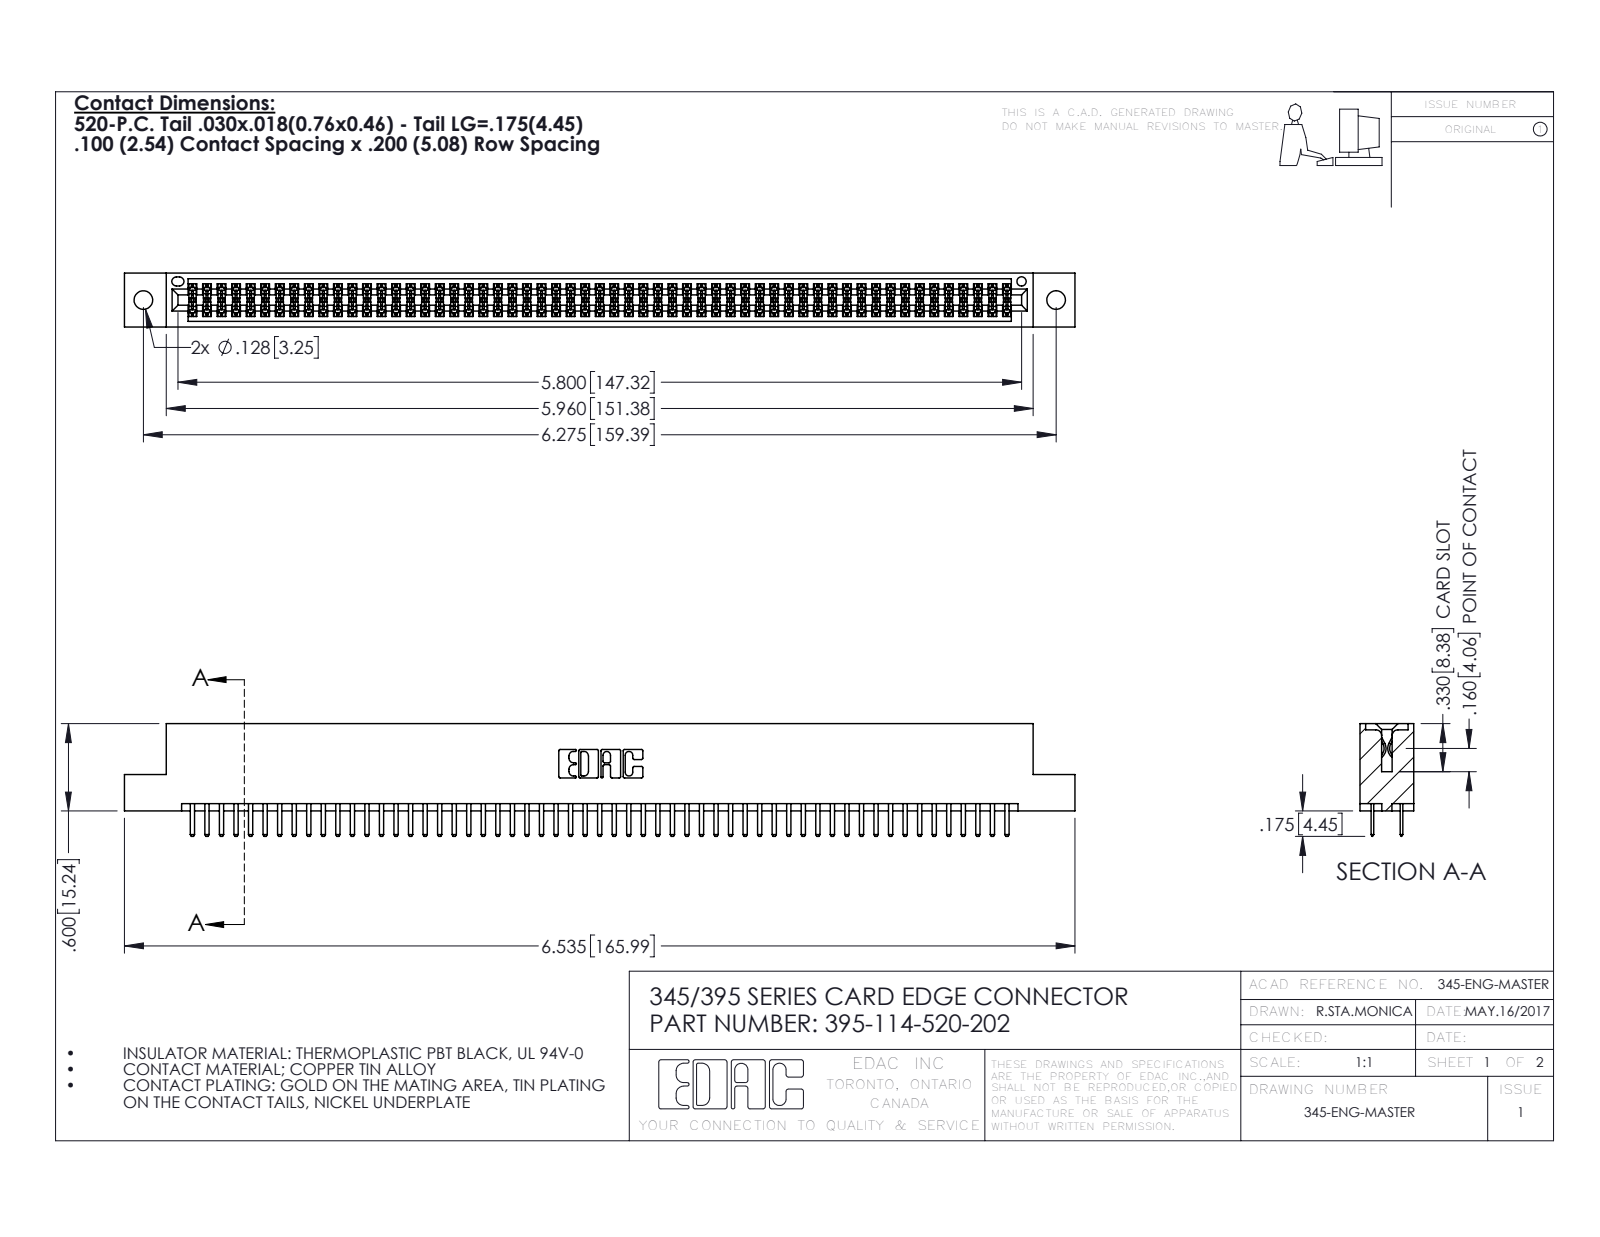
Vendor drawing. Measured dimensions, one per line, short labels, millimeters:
name: 345-292-001_345-293-120; 345 Part_Flush Mounting Lugs - 0.128 Dia; 395-114-520-202
written by: SolidWorks 2016 (CONFIG_CONTROL_DESIGN)
unit: mm
bodies: 115 solids, 6282 faces (4070 planar, 2212 cylindrical, 0 other)
size: 166 × 19.7 × 9.4
volume: 16 200 mm³; area: 23 830 mm²
holes: 2× ⌀3.3, 1× ⌀1.6
rounds: 171× R0.2, 118× R0.3, 22× R0.3, 6× R0.2, 6× R0.8, 3× R0.7, 2× R0.4, 2× R0.5
face distances: 7.6, 1.8, 5.1, 9.4, 2.5, 6.9, 0.6, 5.7, 0.6, 1.8
hole spacings: 6.9, 153.4, 159.4
